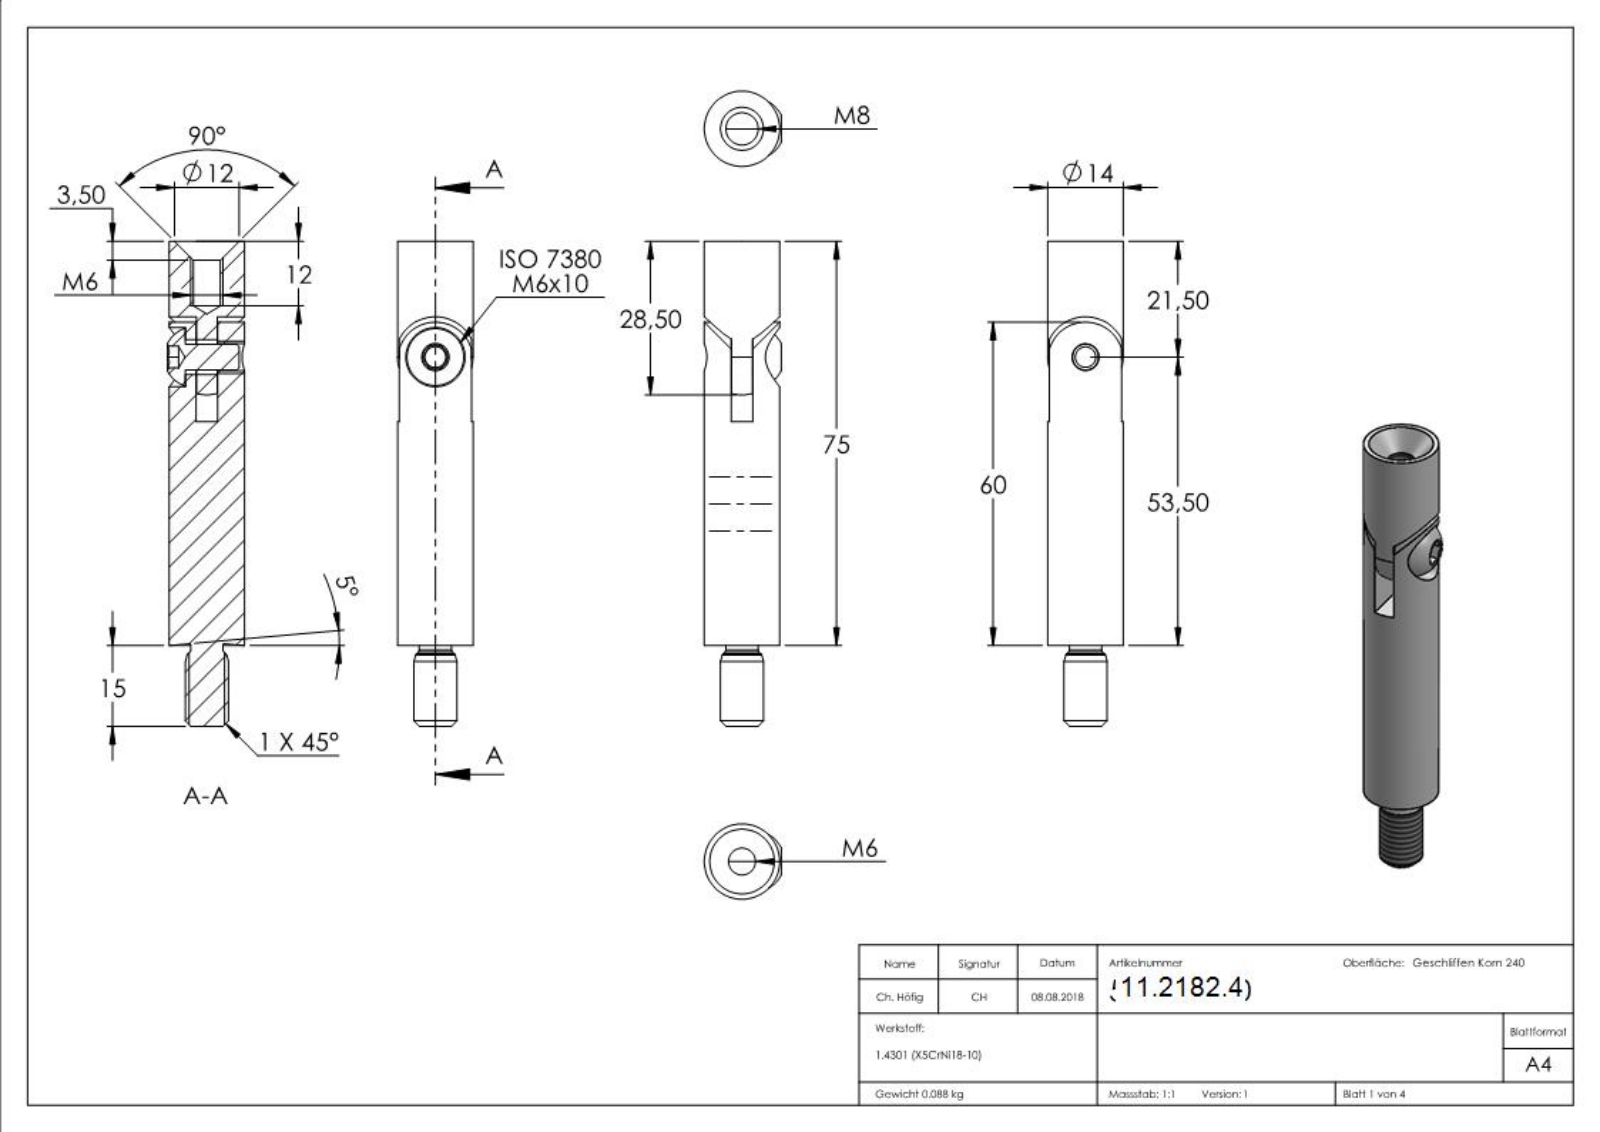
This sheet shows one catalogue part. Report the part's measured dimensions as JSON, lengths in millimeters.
{"part_name": "50232-240 Teil3_ISO 7380 M6x10; 50232-240 Teil2_50232-240 Teil2; 50232-240 Teil1_50232-240 Teil1; 50232-240", "step_written_by": "SolidWorks 2015 (CONFIG_CONTROL_DESIGN)", "units": "millimeters", "bodies": {"solids": 3, "faces": 79, "planar": 18, "cylindrical": 26, "other": 35}, "overall_size": [90, 14.3, 14], "volume_mm3": 11184, "surface_area_mm2": 5641, "round_holes": [[5, 2], [6.5, 1], [11, 1]], "round_bosses_or_shafts": [[14, 1], [10.6, 1], [8, 1], [6, 1], [4.77, 1]], "partial_cylinders_radius": [[7, 1], [7.5, 1]], "face_to_face_distances": [3.95, 4, 6, 2, 5.95, 3.9, 2.05, 33.5, 56.5, 90]}
